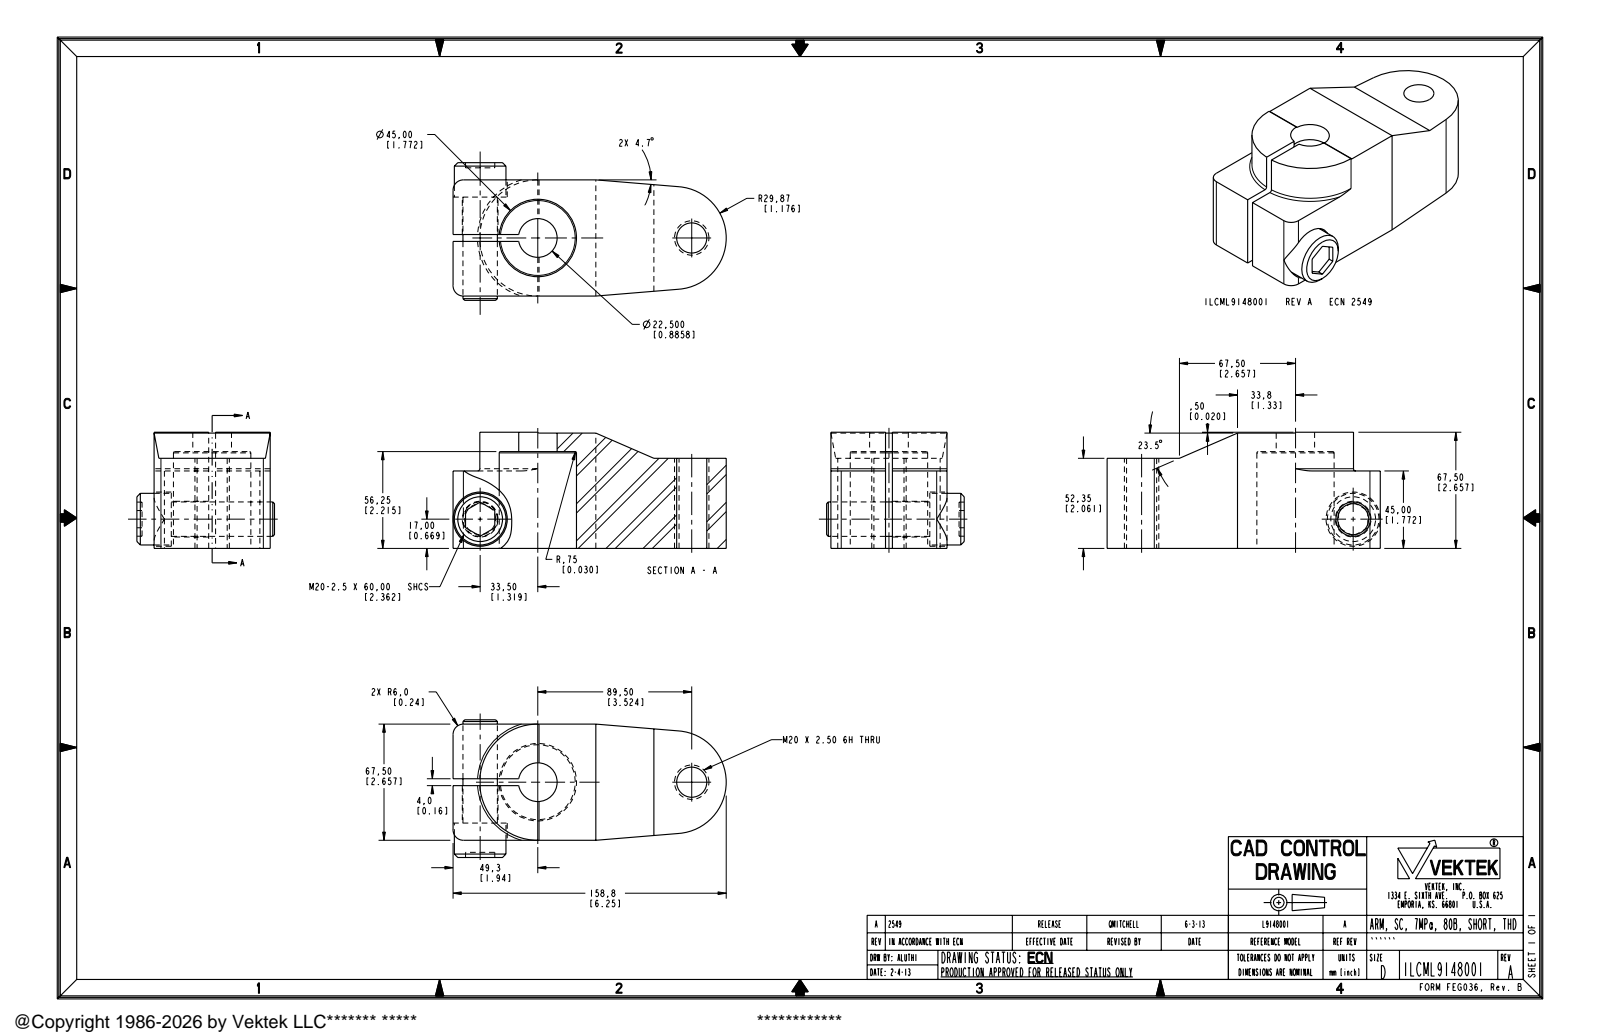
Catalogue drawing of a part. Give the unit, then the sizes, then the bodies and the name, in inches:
Units: inches
Overall size (bounding box): 6.252 × 3.15 × 2.657
Round holes (diameter × count): ⌀0.689 ×1, ⌀0.817 ×1, ⌀0.886 ×1, ⌀1.24 ×1, ⌀1.772 ×1
Round bosses / shafts (diameter × count): ⌀0.787 ×2, ⌀1.181 ×1
Partial cylindrical surfaces — rounded edges, fillets, slot ends (radius × count): R0.236 ×2, R0.031 ×1, R1.176 ×1, R1.329 ×1
Main face-to-face distances: 2.657, 1.25, 1.407, 0.443, 2.638, 2.061, 0.577, 0.596, 0.02, 1.772
Hole centre spacings: 3.524
Volume: 29.22 in³ · Surface area: 104.8 in²
Bodies: 1 solid, 61 faces (28 planar, 26 cylindrical, 7 other)
Part name (STEP PRODUCT): ILCML9148001
STEP written by: PRO/ENGINEER BY PARAMETRIC TECHNOLOGY CORPORATION, 2007460 (AUTOMOTIVE_DESIGN_CC2)
